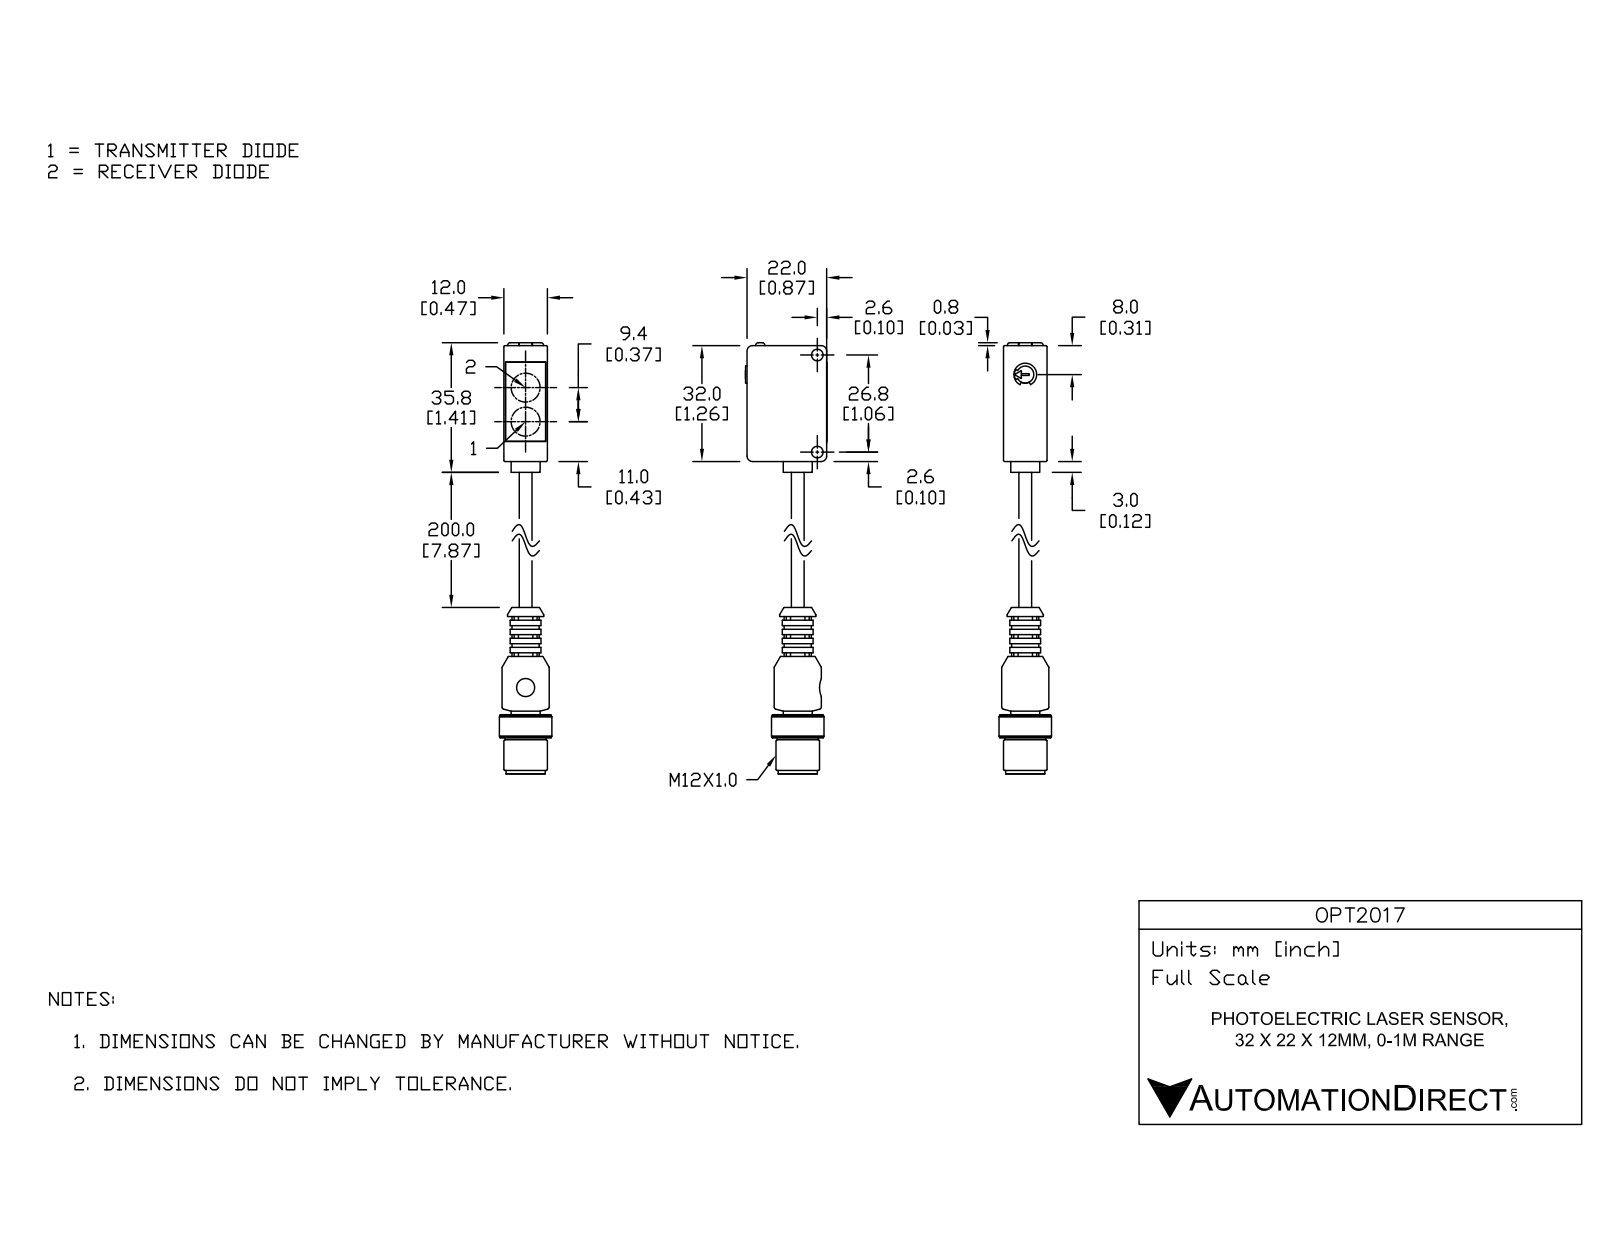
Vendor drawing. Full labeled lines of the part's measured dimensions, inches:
Part name (STEP PRODUCT): Dummy Klebstoff
STEP written by: Unknown (AUTOMOTIVE_DESIGN)
Units: inches
Bodies: 2 solids, 281 faces (148 planar, 93 cylindrical, 40 other)
Overall size (bounding box): 4.689 × 0.886 × 0.571
Volume: 0.789 in³ · Surface area: 9.703 in²
Round holes (diameter × count): ⌀0.126 ×2, ⌀0.197 ×1, ⌀0.248 ×1, ⌀0.354 ×1
Round bosses / shafts (diameter × count): ⌀0.039 ×4, ⌀0.571 ×1, ⌀0.561 ×1, ⌀0.512 ×1, ⌀0.472 ×1, ⌀0.443 ×1, ⌀0.425 ×1, ⌀0.394 ×1
Partial cylindrical surfaces — rounded edges, fillets, slot ends (radius × count): R0.012 ×8, R0.02 ×5, R0.039 ×4, R0.059 ×4, R0.004 ×2, R0.028 ×2, R0.049 ×2, R0.075 ×1
Main face-to-face distances: 0.472, 0.87, 1.26, 0.098, 0.197, 0.039, 0.866, 2.752, 4.012, 0.02
Hole centre spacings: 1.055, 3.402
